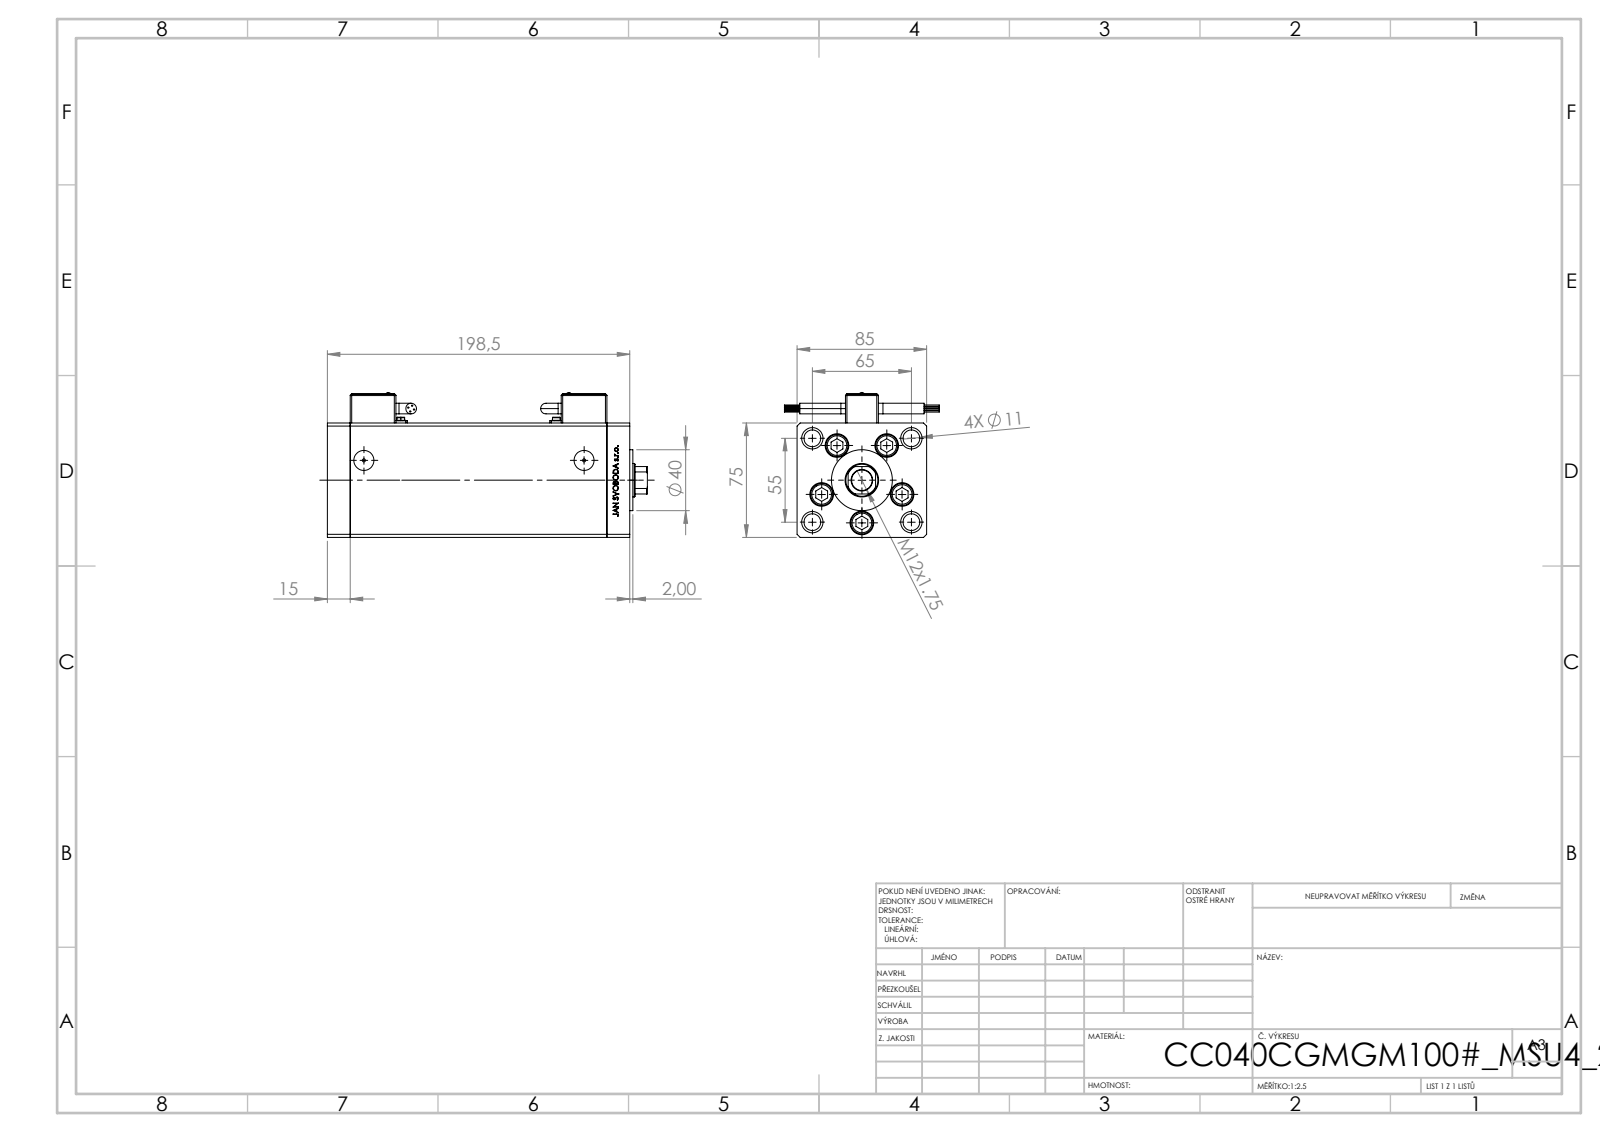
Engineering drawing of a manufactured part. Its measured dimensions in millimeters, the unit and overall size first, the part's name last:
Units: millimetres
Overall size (bounding box): 210 × 101.6 × 95.1
Round holes (diameter × count): ⌀11 ×9, ⌀15.5 ×5, ⌀10 ×4, ⌀14 ×4, ⌀2 ×2, ⌀3.6 ×2, ⌀5 ×2, ⌀7 ×2, ⌀13.16 ×2, ⌀13.5 ×1, ⌀14.5 ×1, ⌀22 ×1
Round bosses / shafts (diameter × count): ⌀0.85 ×8, ⌀8 ×5, ⌀14.5 ×4, ⌀7 ×4, ⌀6 ×2, ⌀3.5 ×2, ⌀2.5 ×2, ⌀40 ×1
Partial cylindrical surfaces — rounded edges, fillets, slot ends (radius × count): R1 ×24, R4 ×4, R0.93 ×2, R10.5 ×1
Main face-to-face distances: 85, 75, 168.5, 15, 183.5, 10.5, 68.5, 198.5, 34.25, 6.5
Hole centre spacings: 28, 42.57, 8.25, 16.86, 19.17, 32.33, 32.5, 33.63
Volume: 1 083 000 mm³ · Surface area: 205 410 mm²
Bodies: 15 solids, 1379 faces (624 planar, 257 cylindrical, 498 other)
Part name (STEP PRODUCT): V220C BACK_C; ALLEN BOLT; V220C FRONT; Magnetic_Switch_MSU4 (+2 more)
STEP written by: SolidWorks 2019 (CONFIG_CONTROL_DESIGN)
